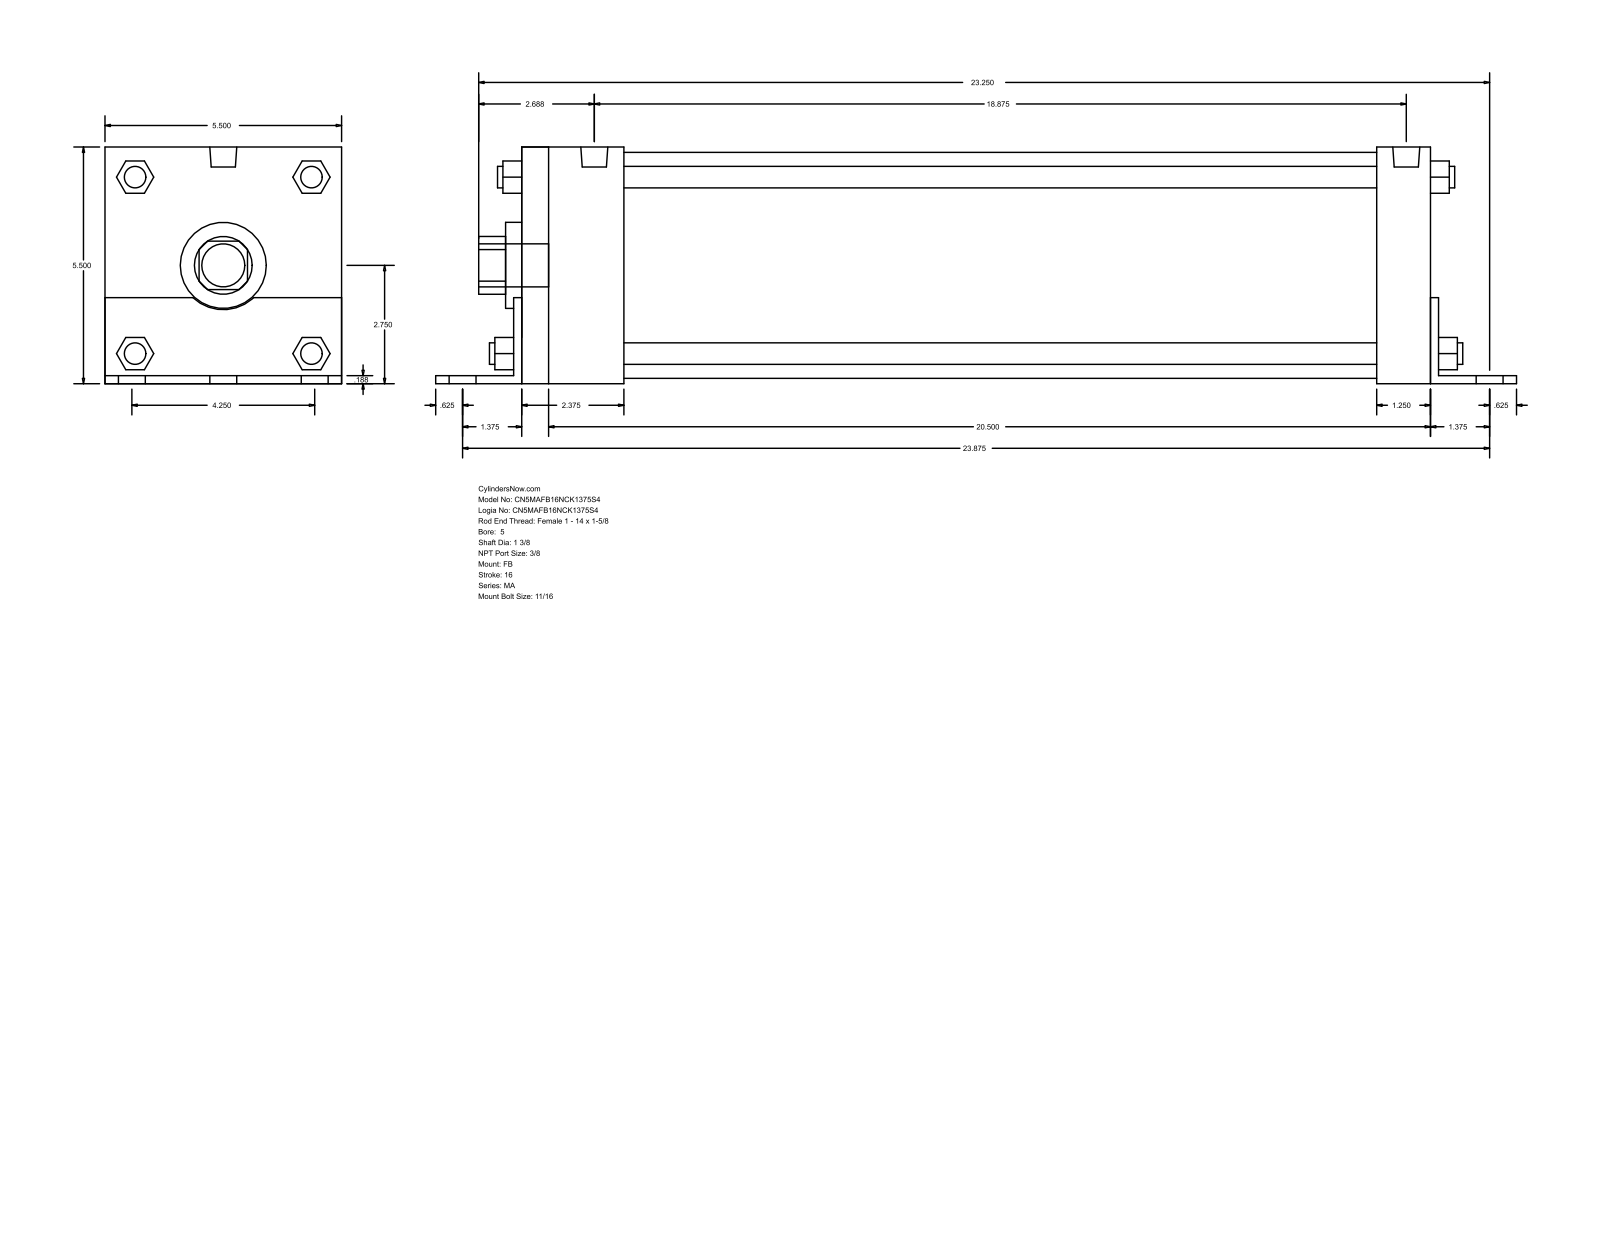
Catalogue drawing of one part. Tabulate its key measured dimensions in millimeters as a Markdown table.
| quantity | value |
| --- | --- |
| part name | MA_FB__0500_1.375 |
| STEP written by | GSSL Pune (CONFIG_CONTROL_DESIGN) |
| units | millimeters |
| bodies | 0 solids, 140 faces (105 planar, 35 cylindrical, 0 other) |
| overall size | 638.17 × 139.75 × 139.7 |
| round holes (diameter × count) | 34.92 × 1, 50.8 × 1, 133.35 × 1 |
| round bosses / shafts (diameter × count) | 17.46 × 6, 12.7 × 4, 11.11 × 4, 15.93 × 2, 25.4 × 1 |
| partial cylindrical surfaces (radius × count) | 17.06 × 1, 26.16 × 1 |
| main face-to-face distances | 139.7, 4.76, 139.75, 541.34, 4.71, 134.99, 536.58, 546.1, 31.75, 36.51 |
